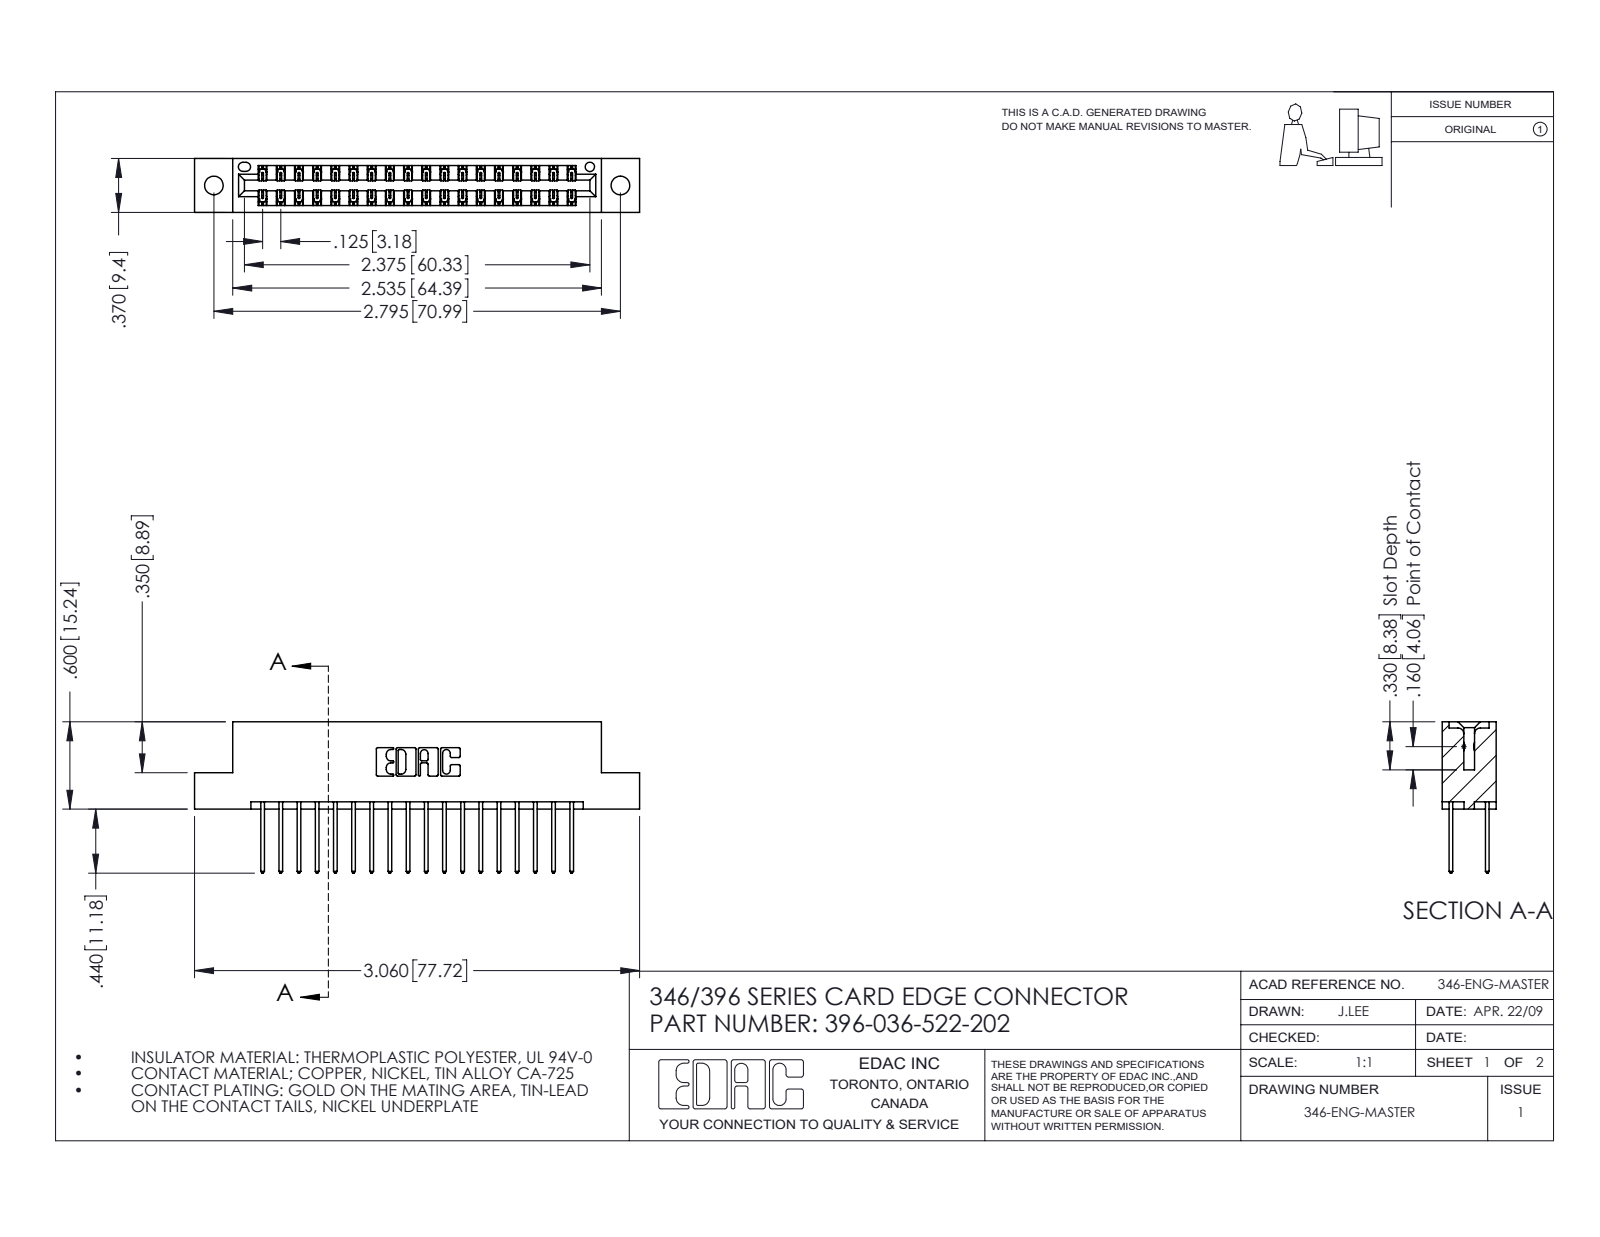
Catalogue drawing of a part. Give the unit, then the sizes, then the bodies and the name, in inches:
Units: inches
Overall size (bounding box): 3.06 × 1.04 × 0.37
Round holes (diameter × count): ⌀0.128 ×2, ⌀0.064 ×1
Partial cylindrical surfaces — rounded edges, fillets, slot ends (radius × count): R0.006 ×54, R0.01 ×36, R0.01 ×22, R0.007 ×6, R0.031 ×6, R0.026 ×3, R0.014 ×2, R0.022 ×2
Main face-to-face distances: 0.048, 0.322, 0.25, 0.37, 0.072, 0.298, 0.025, 0.275, 0.148, 0.222
Hole centre spacings: 0.246, 2.588, 2.795
Volume: 0.455 in³ · Surface area: 15.53 in²
Bodies: 37 solids, 1994 faces (1336 planar, 658 cylindrical, 0 other)
Part name (STEP PRODUCT): 346 Part_Flush Mounting Lugs - 0.128 Dia; 396-036-522-202; 345-292-001_345-293-122
STEP written by: SolidWorks 2016 (CONFIG_CONTROL_DESIGN)
